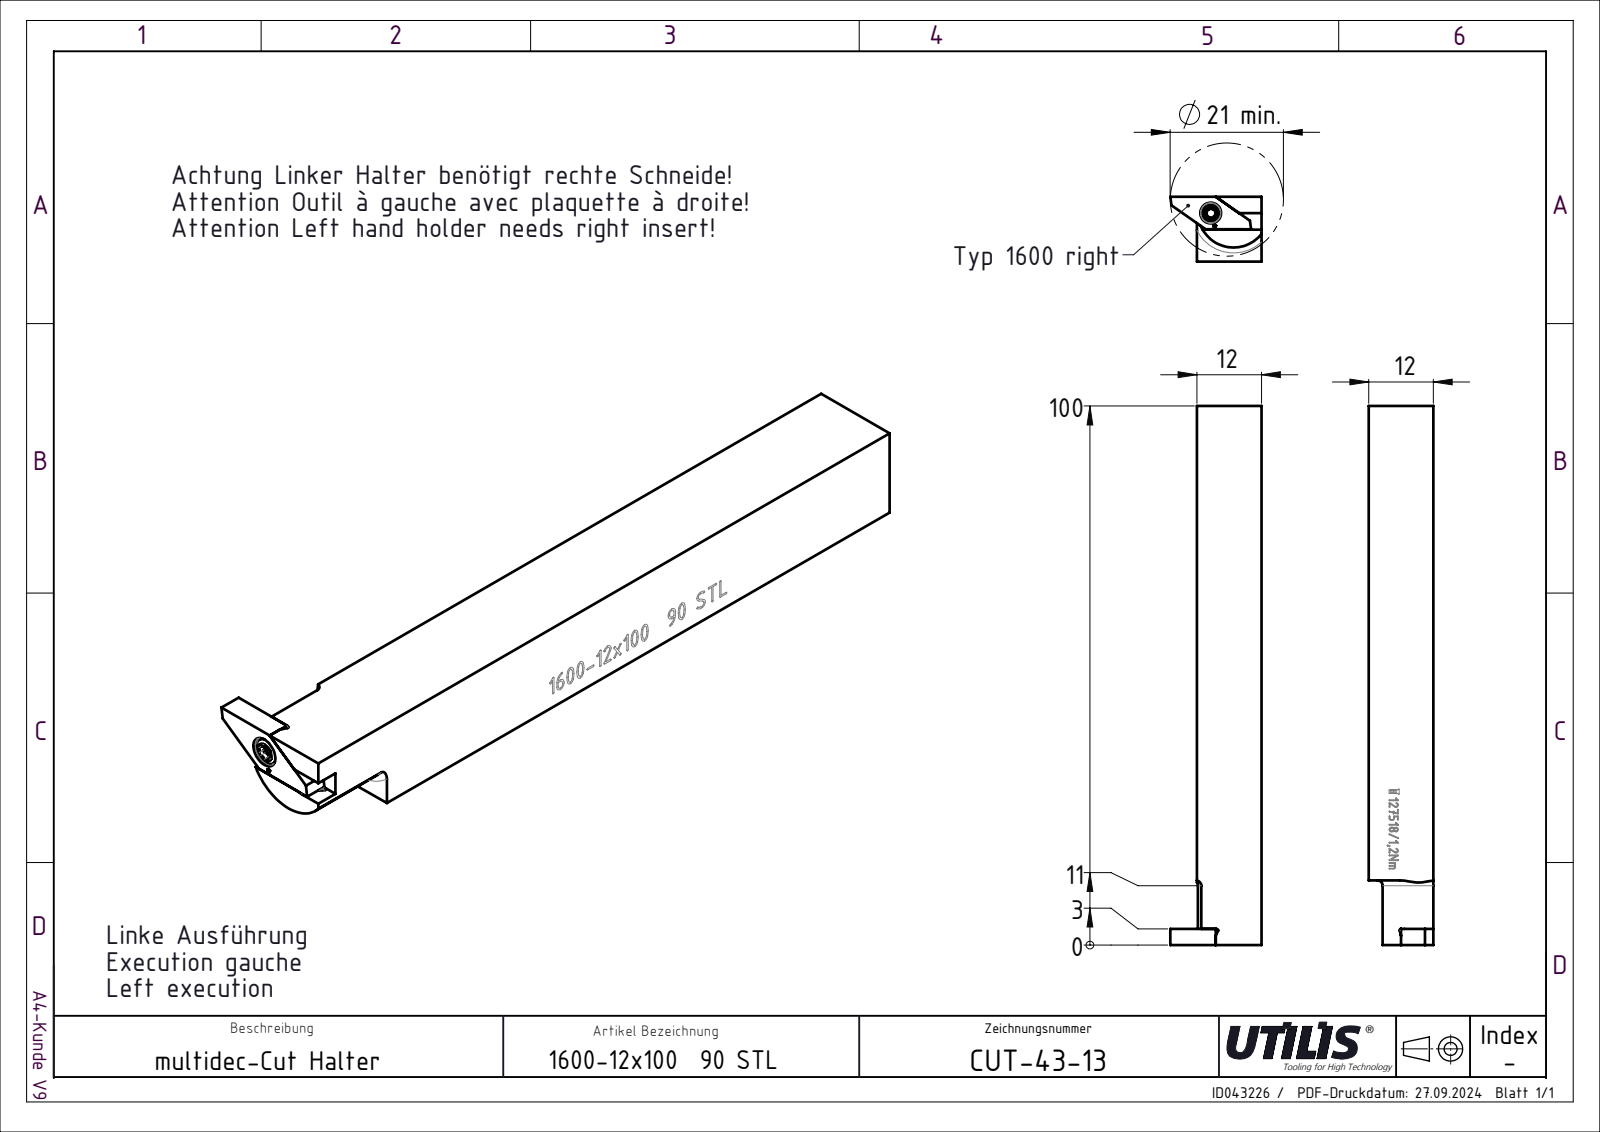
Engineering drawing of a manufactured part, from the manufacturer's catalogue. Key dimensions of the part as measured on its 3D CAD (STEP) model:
Part name (STEP PRODUCT): CUT-43-Platte-Kunde_Dfaut; CUT-43-Kunde_12 L; CUT-43-13; MSP-7_M2,5X7-TX8 CERATIZIT Schraube
STEP written by: SolidWorks 2013 (CONFIG_CONTROL_DESIGN)
Units: millimetres
Bodies: 3 solids, 79 faces (24 planar, 29 cylindrical, 26 other)
Overall size (bounding box): 100 × 17.5 × 12
Volume: 13 993 mm³ · Surface area: 5 344 mm²
Round holes (diameter × count): ⌀2.05 ×1, ⌀3 ×1
Round bosses / shafts (diameter × count): ⌀3.45 ×1, ⌀2.5 ×1
Partial cylindrical surfaces — rounded edges, fillets, slot ends (radius × count): R0.2 ×6, R0.45 ×6, R0.4 ×2, R2.9 ×2, R6.6 ×1
Main face-to-face distances: 12, 100, 6, 97, 3, 88, 9, 6.01, 2.73, 15.01
